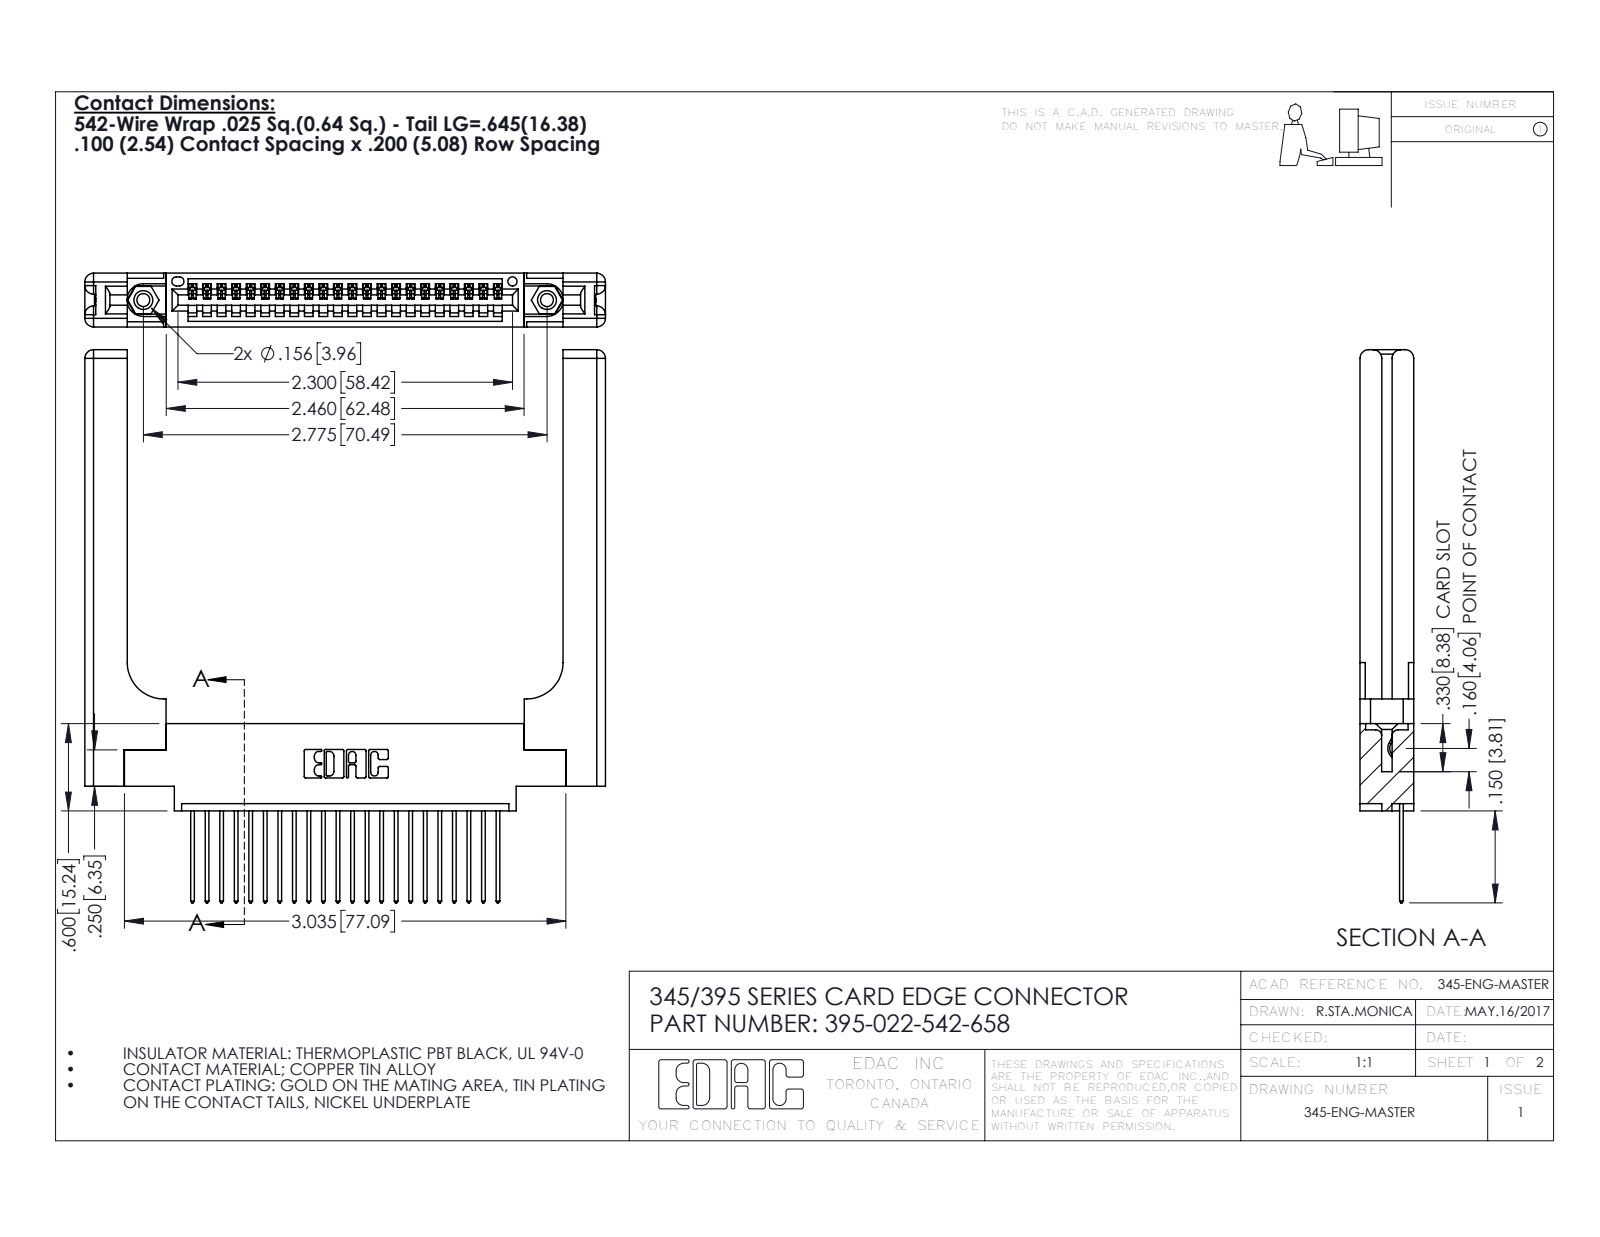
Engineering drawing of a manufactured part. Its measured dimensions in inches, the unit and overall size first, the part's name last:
Units: inches
Overall size (bounding box): 3.802 × 3.579 × 0.37
Round holes (diameter × count): ⌀0.089 ×2, ⌀0.125 ×2, ⌀0.156 ×2, ⌀0.064 ×1
Round bosses / shafts (diameter × count): ⌀0.155 ×2
Partial cylindrical surfaces — rounded edges, fillets, slot ends (radius × count): R0.006 ×44, R0.01 ×44, R0.01 ×22, R0.06 ×16, R0.007 ×6, R0.031 ×6, R0.026 ×3, R0.03 ×2
Main face-to-face distances: 0.37, 0.072, 0.298, 0.15, 0.148, 0.098, 0.272, 0.025, 0.077, 0.2
Hole centre spacings: 0.27, 2.541, 2.775
Volume: 1.032 in³ · Surface area: 25.79 in²
Bodies: 27 solids, 1662 faces (1112 planar, 490 cylindrical, 60 other)
Part name (STEP PRODUCT): 345-292-001_345-293-142; 345-250-001_345-250-001-102; 395-022-542-658; 345-220-058_345-220-058 (+1 more)
STEP written by: SolidWorks 2016 (CONFIG_CONTROL_DESIGN)
